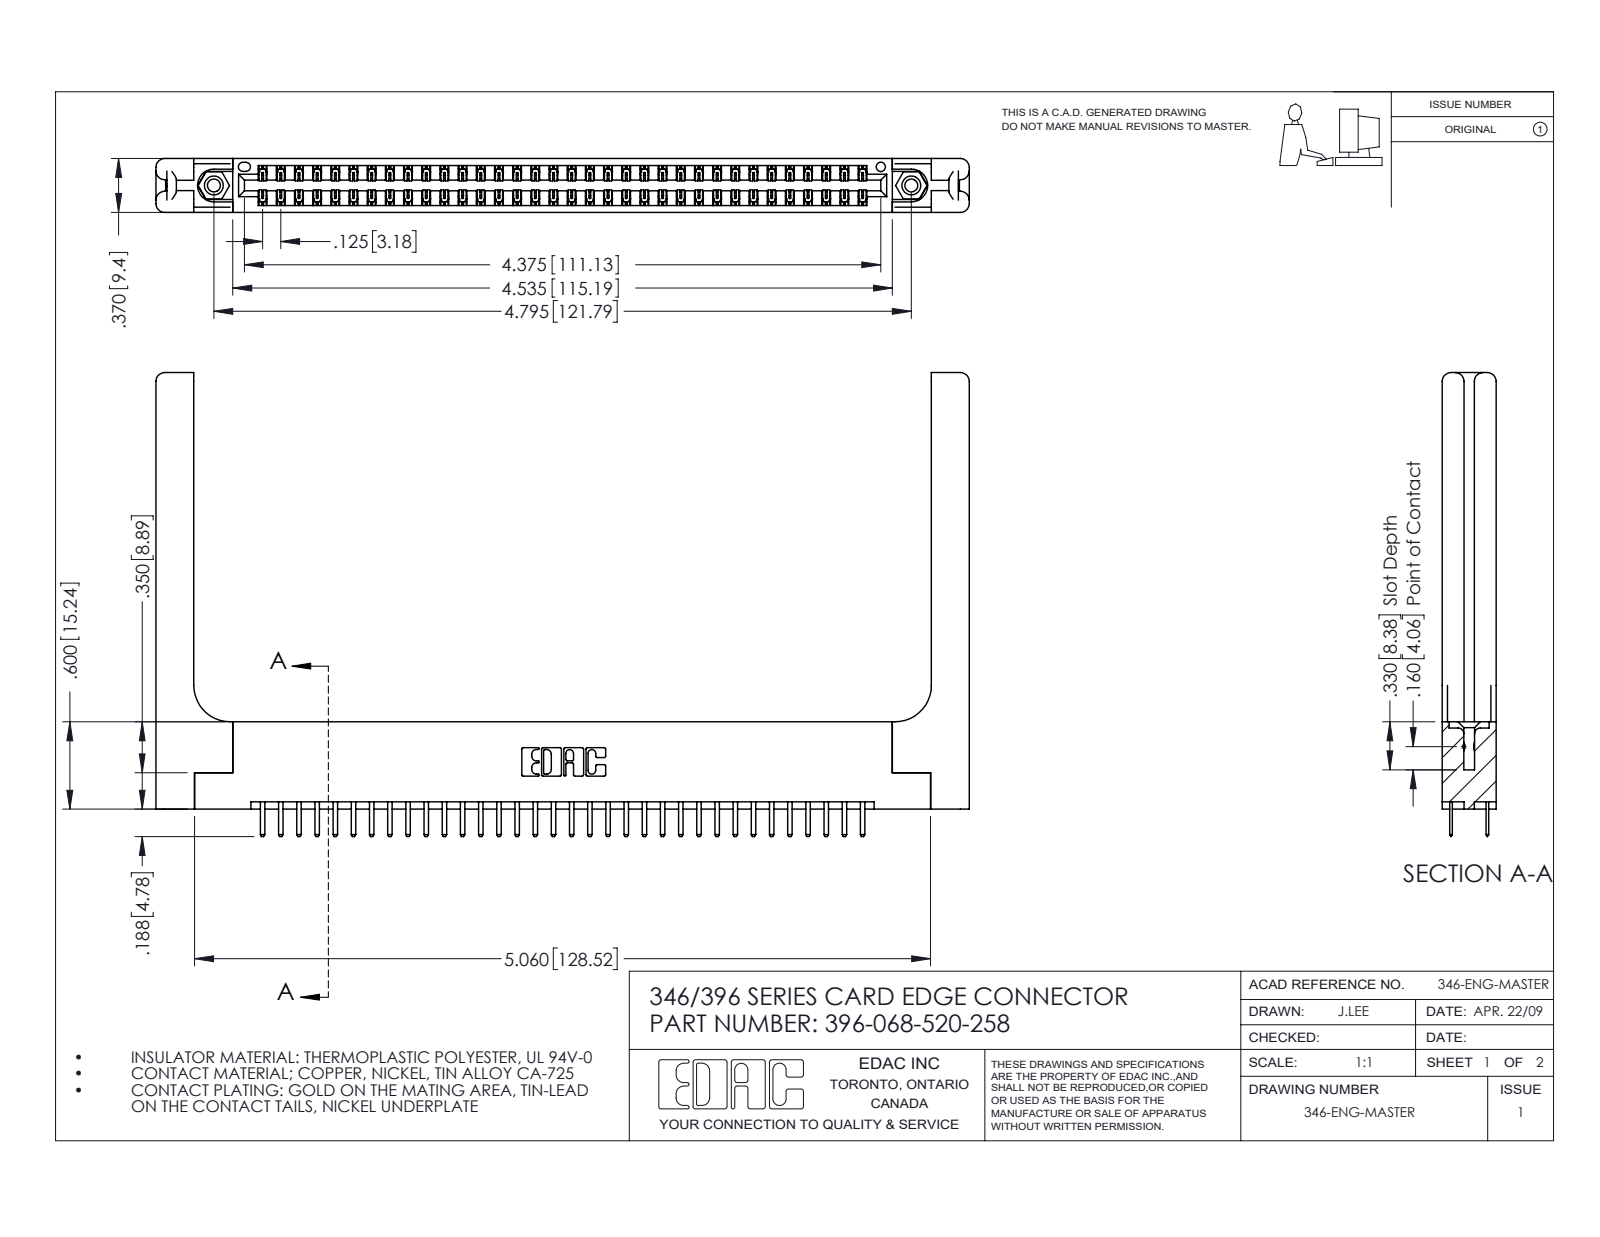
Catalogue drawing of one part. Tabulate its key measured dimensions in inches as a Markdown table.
| quantity | value |
| --- | --- |
| part name | 345-292-001_345-293-120; 396-068-520-258; 346 Part_Flush Mounting Lugs - 0.156 Dia-TH; 346-220-058_345-220-058 (+1 more) |
| STEP written by | SolidWorks 2016 (CONFIG_CONTROL_DESIGN) |
| units | inches |
| bodies | 73 solids, 4186 faces (2740 planar, 1386 cylindrical, 60 other) |
| overall size | 5.591 × 3.188 × 0.37 |
| volume | 1.297 in³ |
| surface area | 36.71 in² |
| round holes (diameter × count) | 0.089 × 2, 0.125 × 2, 0.156 × 2, 0.064 × 1 |
| round bosses / shafts (diameter × count) | 0.155 × 2 |
| partial cylindrical surfaces (radius × count) | 0.006 × 102, 0.01 × 72, 0.01 × 22, 0.06 × 16, 0.007 × 6, 0.031 × 6, 0.026 × 3, 0.014 × 2 |
| main face-to-face distances | 0.37, 0.048, 0.322, 0.072, 0.25, 0.148, 0.15, 0.298, 0.025, 0.275 |
| hole center spacings | 0.246, 4.587, 4.795 |
